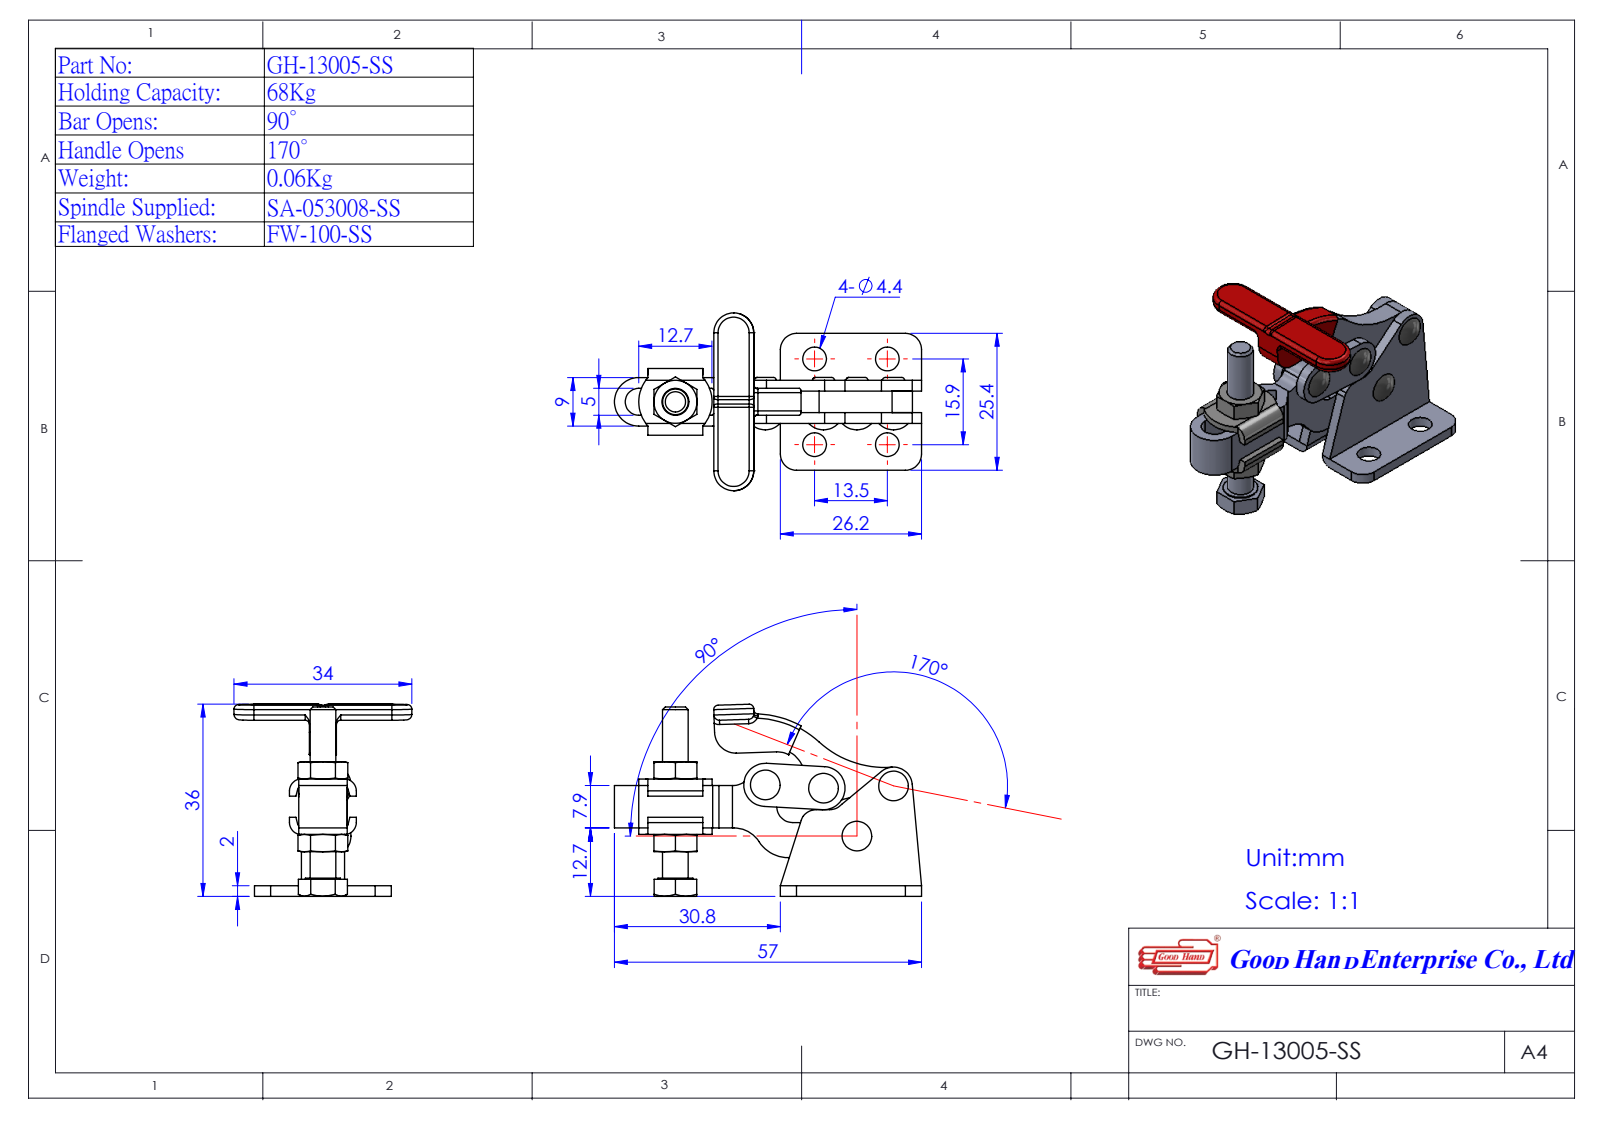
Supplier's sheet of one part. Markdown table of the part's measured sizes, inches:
| quantity | value |
| --- | --- |
| part name | 11300501-2^GH-13005-SS(簡化); GH-13005-SS(簡化); Group4^GH-13005-SS(簡化); 11300508-1^GH-13005-SS(簡化) (+2 more) |
| STEP written by | SolidWorks 2016 (AUTOMOTIVE_DESIGN) |
| units | inches |
| bodies | 6 solids, 289 faces (133 planar, 108 cylindrical, 48 other) |
| overall size | 2.244 × 1.405 × 1.299 |
| volume | 0.49 in³ |
| surface area | 15.9 in² |
| round holes (diameter × count) | 0.098 × 4, 0.173 × 4 |
| round bosses / shafts (diameter × count) | 0.256 × 1, 0.187 × 1 |
| partial cylindrical surfaces (radius × count) | 0.118 × 9, 0.039 × 8, 0.087 × 4, 0.138 × 4, 0.157 × 4, 0.04 × 2, 0.059 × 2, 0.067 × 2 |
| main face-to-face distances | 0.079, 0.02, 0.157, 0.236, 0.256, 0.019, 0.315, 0.059, 0.177, 0.091 |
| hole center spacings | 0.531, 0.626, 0.821, 0.426, 0.427, 0.454, 0.512, 0.767 |
